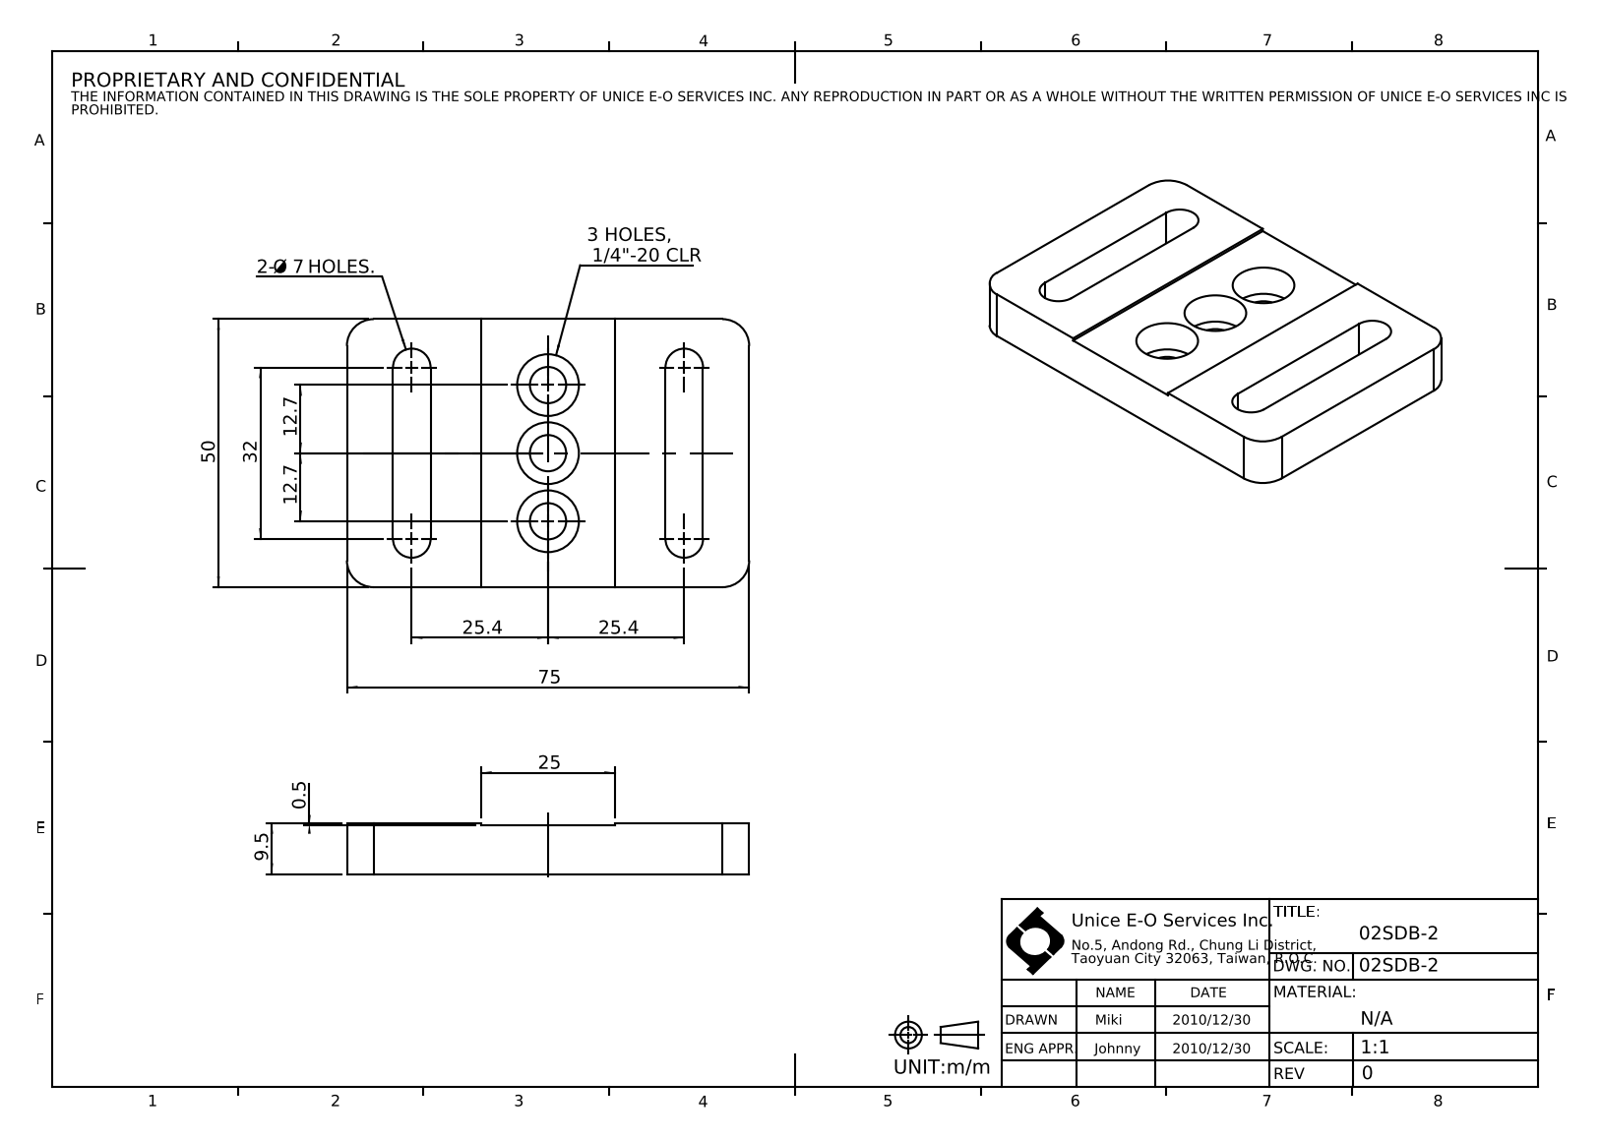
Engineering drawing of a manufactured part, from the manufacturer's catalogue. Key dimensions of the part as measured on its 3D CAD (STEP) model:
Part name (STEP PRODUCT): 02SDB-2
STEP written by: SolidWorks 2016 (CONFIG_CONTROL_DESIGN)
Units: millimetres
Bodies: 1 solid, 39 faces (17 planar, 22 cylindrical, 0 other)
Overall size (bounding box): 75 × 50 × 9.5
Volume: 27 610 mm³ · Surface area: 10 987 mm²
Round holes (diameter × count): ⌀6.76 ×3, ⌀11.51 ×3
Partial cylindrical surfaces — rounded edges, fillets, slot ends (radius × count): R3.5 ×4, R5 ×4
Main face-to-face distances: 9.5, 9, 0.5, 50, 8.6, 15.6, 59.4, 66.4, 7, 50.8
Hole centre spacings: 12.7, 25.4
